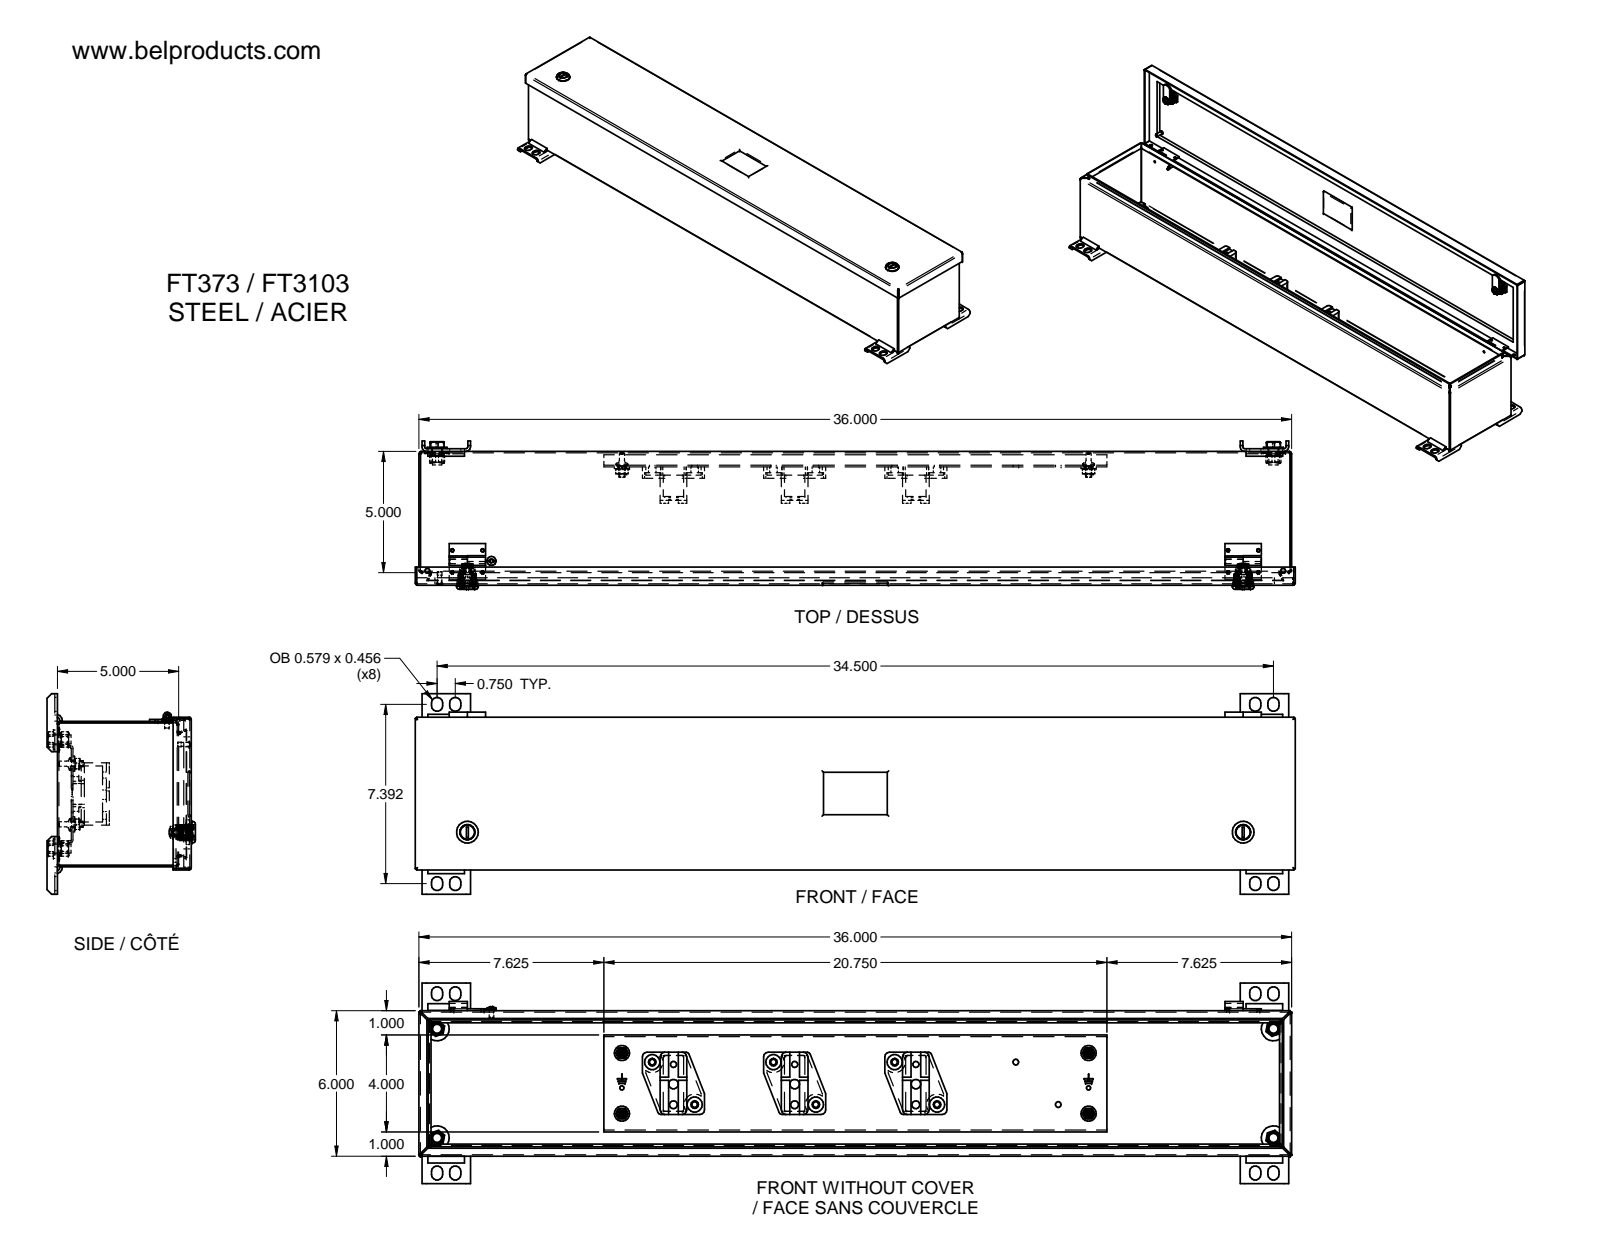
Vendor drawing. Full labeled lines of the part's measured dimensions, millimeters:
Part name (STEP PRODUCT): 0.375 DIA; CAOUTCHOUC; METAL; LOCK AVEC TOURNEVIS TYPE 4-12 SANS CAME-oa8 (+8 more)
STEP written by: Unknown (AUTOMOTIVE_DESIGN)
Units: millimetres
Bodies: 68 solids, 2464 faces (1463 planar, 475 cylindrical, 526 other)
Overall size (bounding box): 922.02 × 209.96 × 155.57
Volume: 1 519 000 mm³ · Surface area: 1 641 000 mm²
Round holes (diameter × count): ⌀3.16 ×8, ⌀3.3 ×8, ⌀5.99 ×8, ⌀9.53 ×8, ⌀11.58 ×8, ⌀6.35 ×7, ⌀7.92 ×6, ⌀15.88 ×6, ⌀3.17 ×5, ⌀7.14 ×4, ⌀9.02 ×4, ⌀10.31 ×4
Round bosses / shafts (diameter × count): ⌀3.17 ×8, ⌀3.02 ×5, ⌀20.62 ×4, ⌀15.88 ×4, ⌀5.56 ×4, ⌀0.79 ×4, ⌀22.86 ×2, ⌀22.61 ×2
Partial cylindrical surfaces — rounded edges, fillets, slot ends (radius × count): R4.76 ×22, R9.53 ×22, R0.81 ×18, R0.25 ×16, R2.34 ×16, R5.79 ×16, R1.46 ×12, R1.52 ×8
Main face-to-face distances: 1.52, 150.88, 1.53, 138.53, 140.06, 137.01, 138.54, 152.4, 149.36, 16.27
Hole centre spacings: 127, 254, 23.03, 177.12, 62.86, 26.99, 31.75, 36.51
